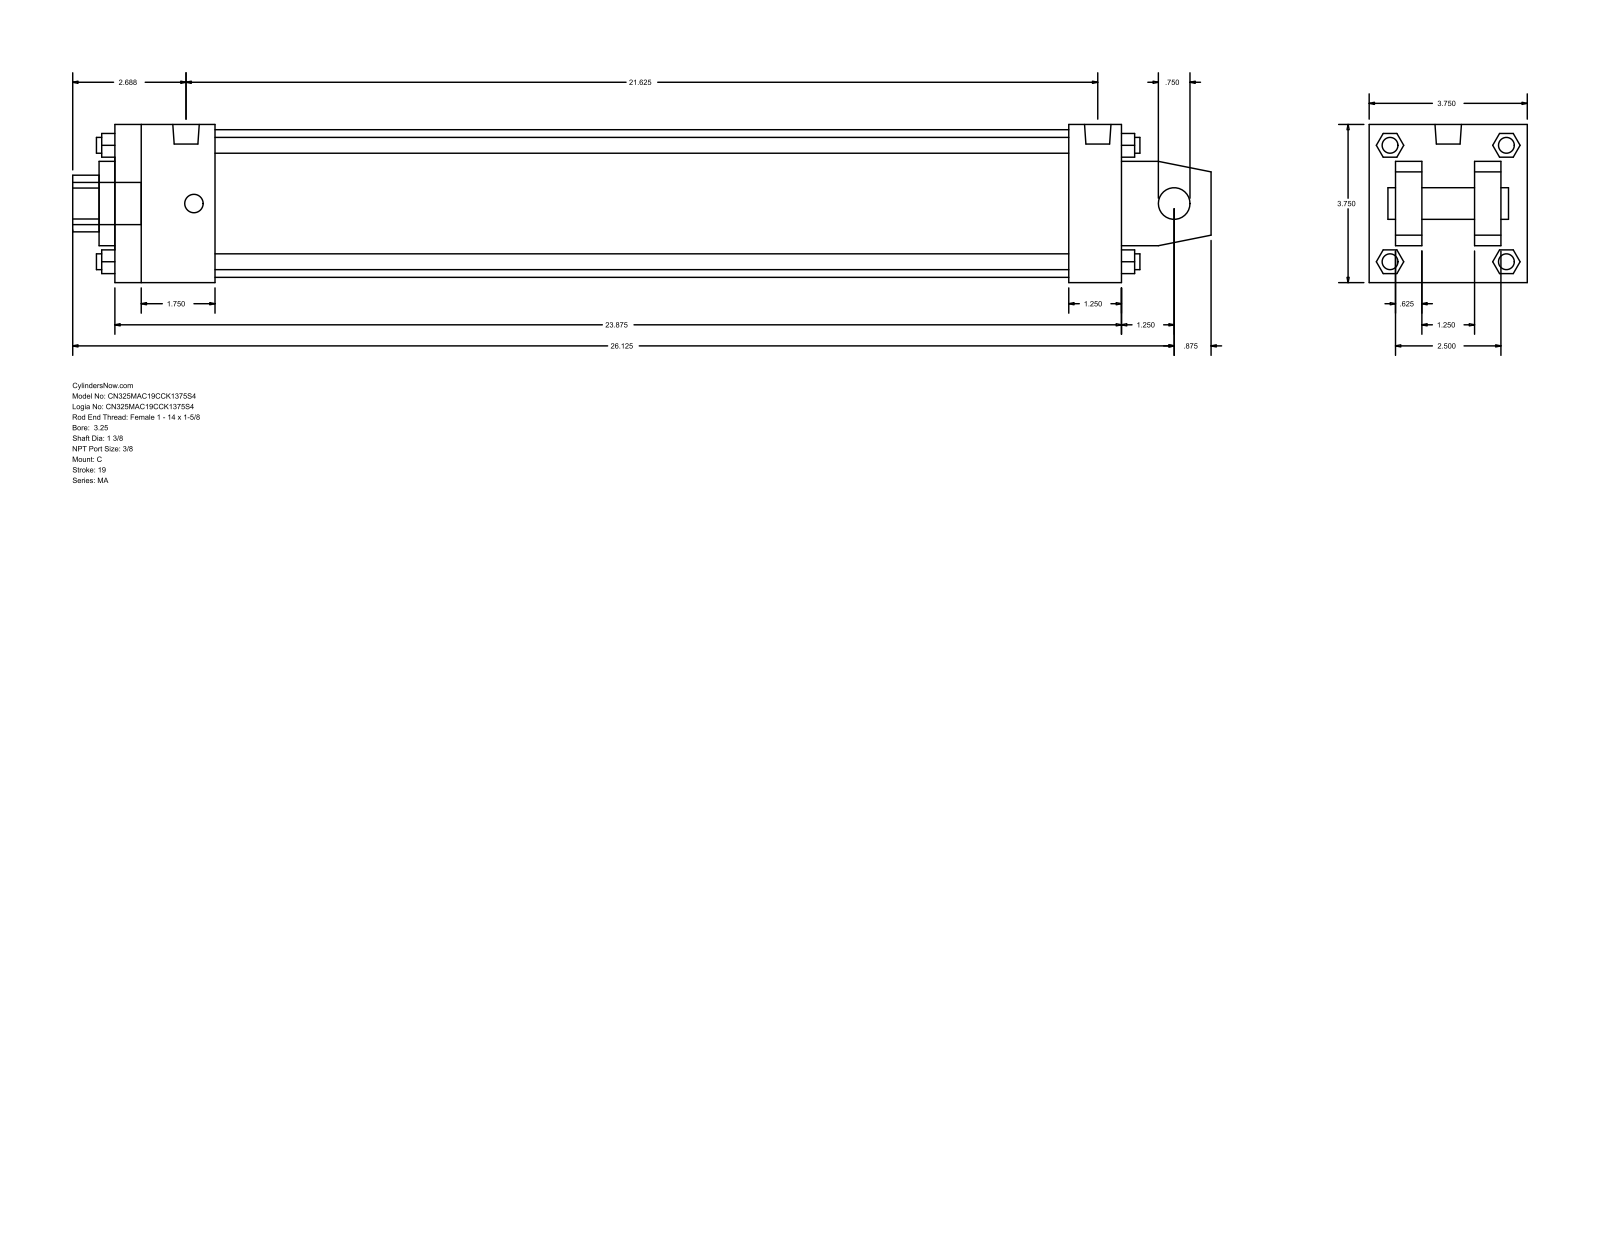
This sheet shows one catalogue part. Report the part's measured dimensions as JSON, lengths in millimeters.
{"part_name": "MA_C__0325_1.375", "step_written_by": "GSSL Pune (CONFIG_CONTROL_DESIGN)", "units": "millimeters", "bodies": {"solids": 0, "faces": 139, "planar": 108, "cylindrical": 31, "other": 0}, "overall_size": [685.8, 95.25, 95.25], "round_holes": [[19.05, 1], [34.92, 1], [50.8, 1], [88.9, 1]], "round_bosses_or_shafts": [[11.11, 4], [9.53, 4], [15.93, 2], [25.4, 1]], "partial_cylinders_radius": [[17.06, 1]], "face_to_face_distances": [95.24, 15.87, 63.5, 606.43, 31.74, 79.37, 47.63, 574.68, 31.75, 60.32]}
